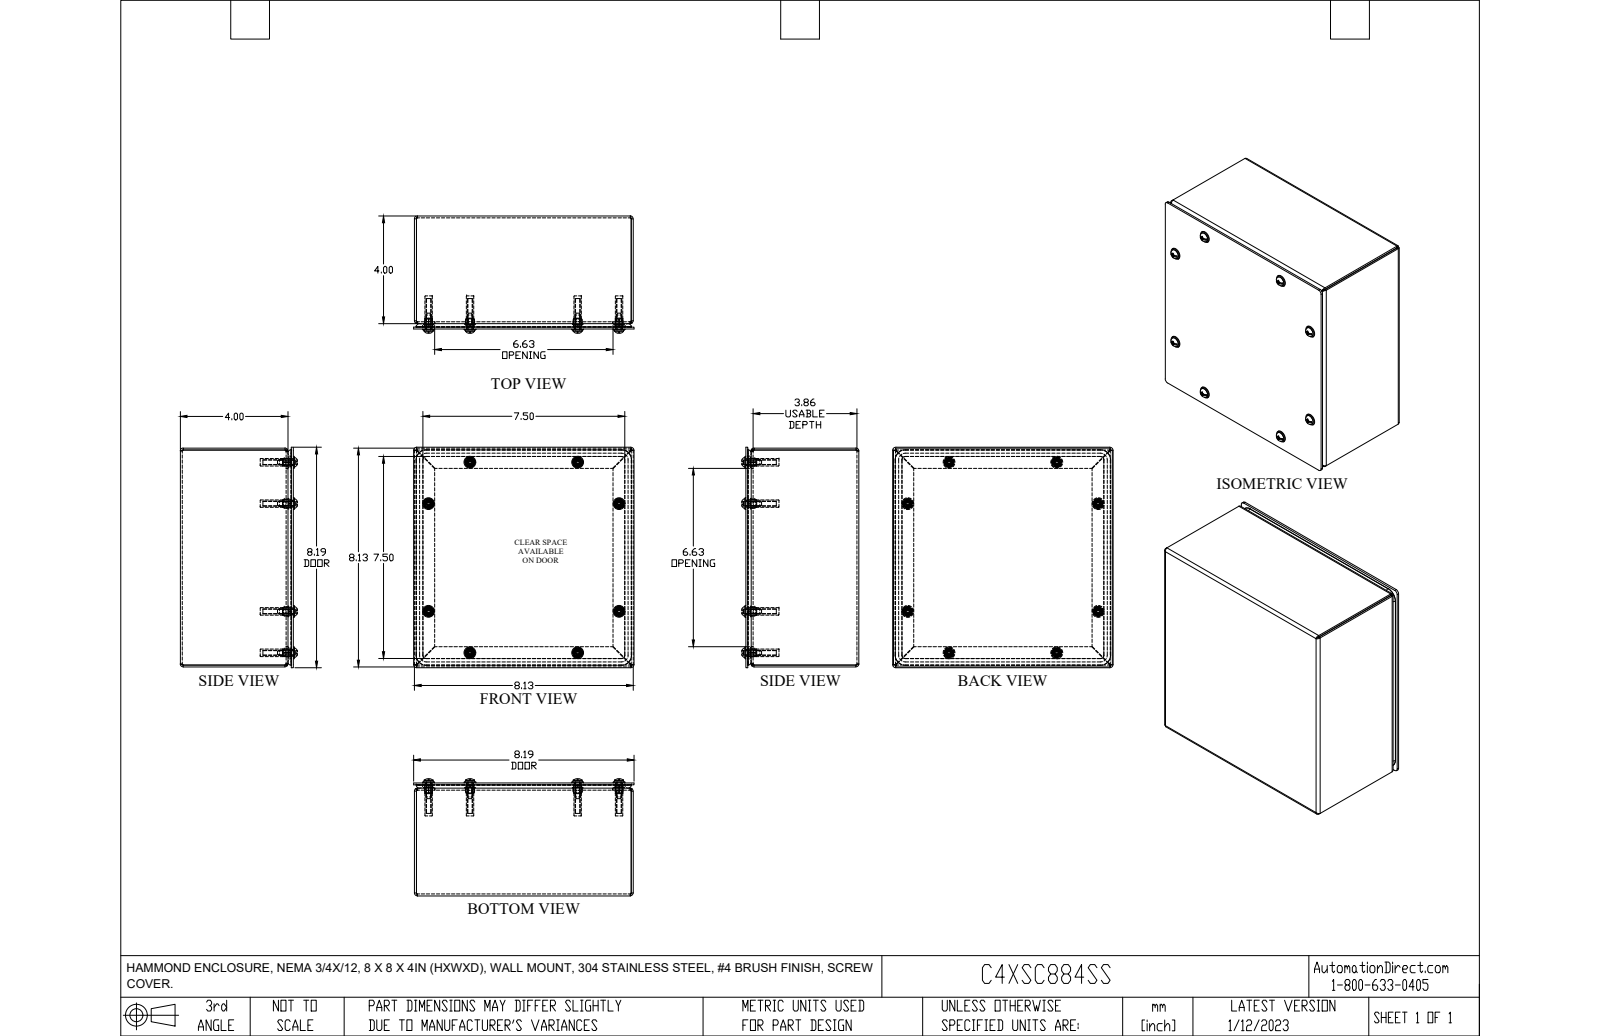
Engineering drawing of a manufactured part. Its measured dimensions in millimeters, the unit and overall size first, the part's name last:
Units: millimetres
Overall size (bounding box): 208 × 208 × 110.4
Round holes (diameter × count): ⌀4 ×8, ⌀4.1 ×8, ⌀6.4 ×8
Round bosses / shafts (diameter × count): ⌀11.2 ×8, ⌀9.9 ×8, ⌀6.1 ×8, ⌀4.8 ×8, ⌀3.8 ×8, ⌀7 ×4, ⌀7 ×4
Partial cylindrical surfaces — rounded edges, fillets, slot ends (radius × count): R1 ×8, R2.8 ×8, R3.2 ×8, R4.1 ×8, R3.2 ×4, R9.5 ×4
Main face-to-face distances: 1.8, 1.8, 104.8, 106.6, 103, 104.8, 206.5, 204.7, 202.9, 204.7
Hole centre spacings: 146, 55.2, 101.6, 179.7, 198.9, 206.4
Volume: 340 400 mm³ · Surface area: 397 900 mm²
Bodies: 27 solids, 780 faces (480 planar, 152 cylindrical, 148 other)
Part name (STEP PRODUCT): C3SC884GY
STEP written by: SolidWorks 2021 (AUTOMOTIVE_DESIGN)
